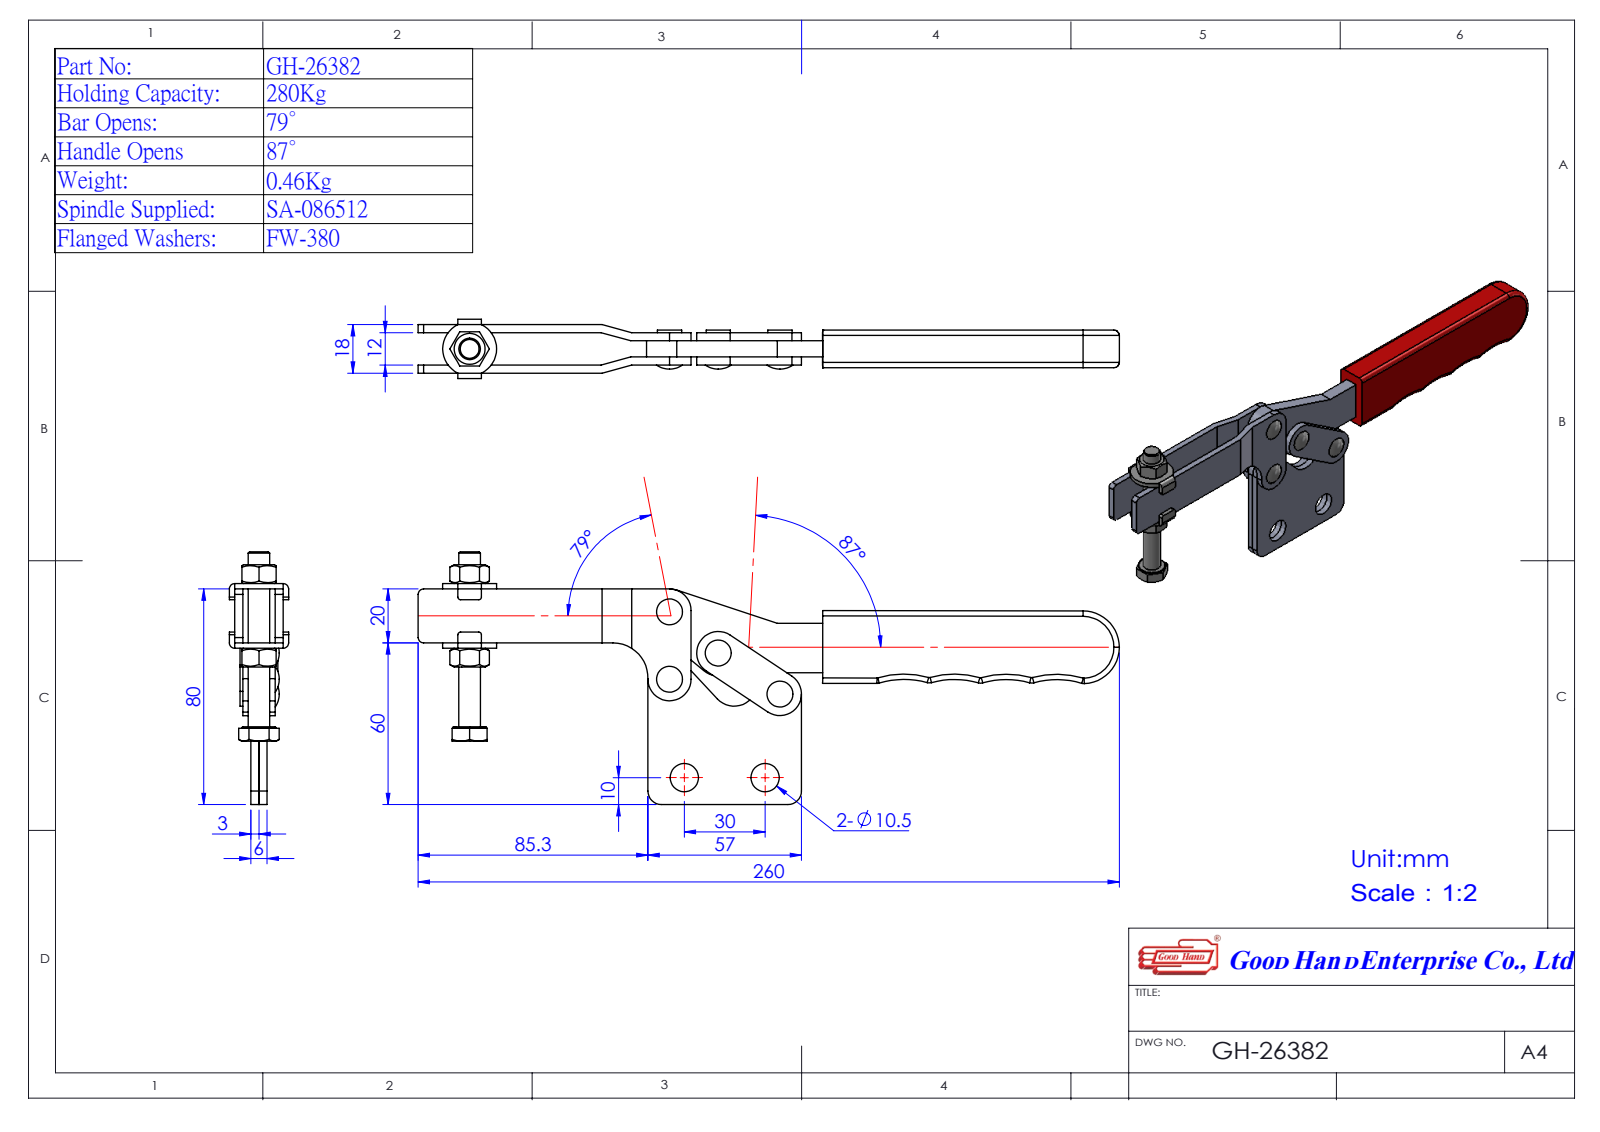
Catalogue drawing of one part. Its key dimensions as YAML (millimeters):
part_name: "Group4^GH-26382(簡化); Group2^GH-26382(簡化)-1; GH-26382(簡化)-1; Group5^GH-26382(簡化)-1 (+2 more)"
step_written_by: "SolidWorks 2016 (AUTOMOTIVE_DESIGN)"
units: millimeters
bodies: {solids: 5, faces: 234, planar: 105, cylindrical: 107, other: 22}
overall_size: [260.27, 93.8, 22]
volume: 87239
surface_area: 38497
round_holes:
  - {diameter: 6, count: 4}
  - {diameter: 10.5, count: 2}
  - {diameter: 5, count: 1}
round_bosses_or_shafts:
  - {diameter: 9, count: 4}
  - {diameter: 16, count: 1}
  - {diameter: 12.5, count: 1}
  - {diameter: 8, count: 1}
partial_cylinders:
  - {radius: 1, count: 8}
  - {radius: 2, count: 6}
  - {radius: 3, count: 5}
  - {radius: 32, count: 4}
  - {radius: 8, count: 3}
  - {radius: 8.5, count: 3}
  - {radius: 5, count: 2}
  - {radius: 10, count: 1}
face_to_face_distances: [3, 6, 4, 10, 12, 13, 9, 1, 2, 16]
hole_center_spacings: [20.55, 23.68, 25, 27.5, 30, 31.48, 36.91, 41.37]
